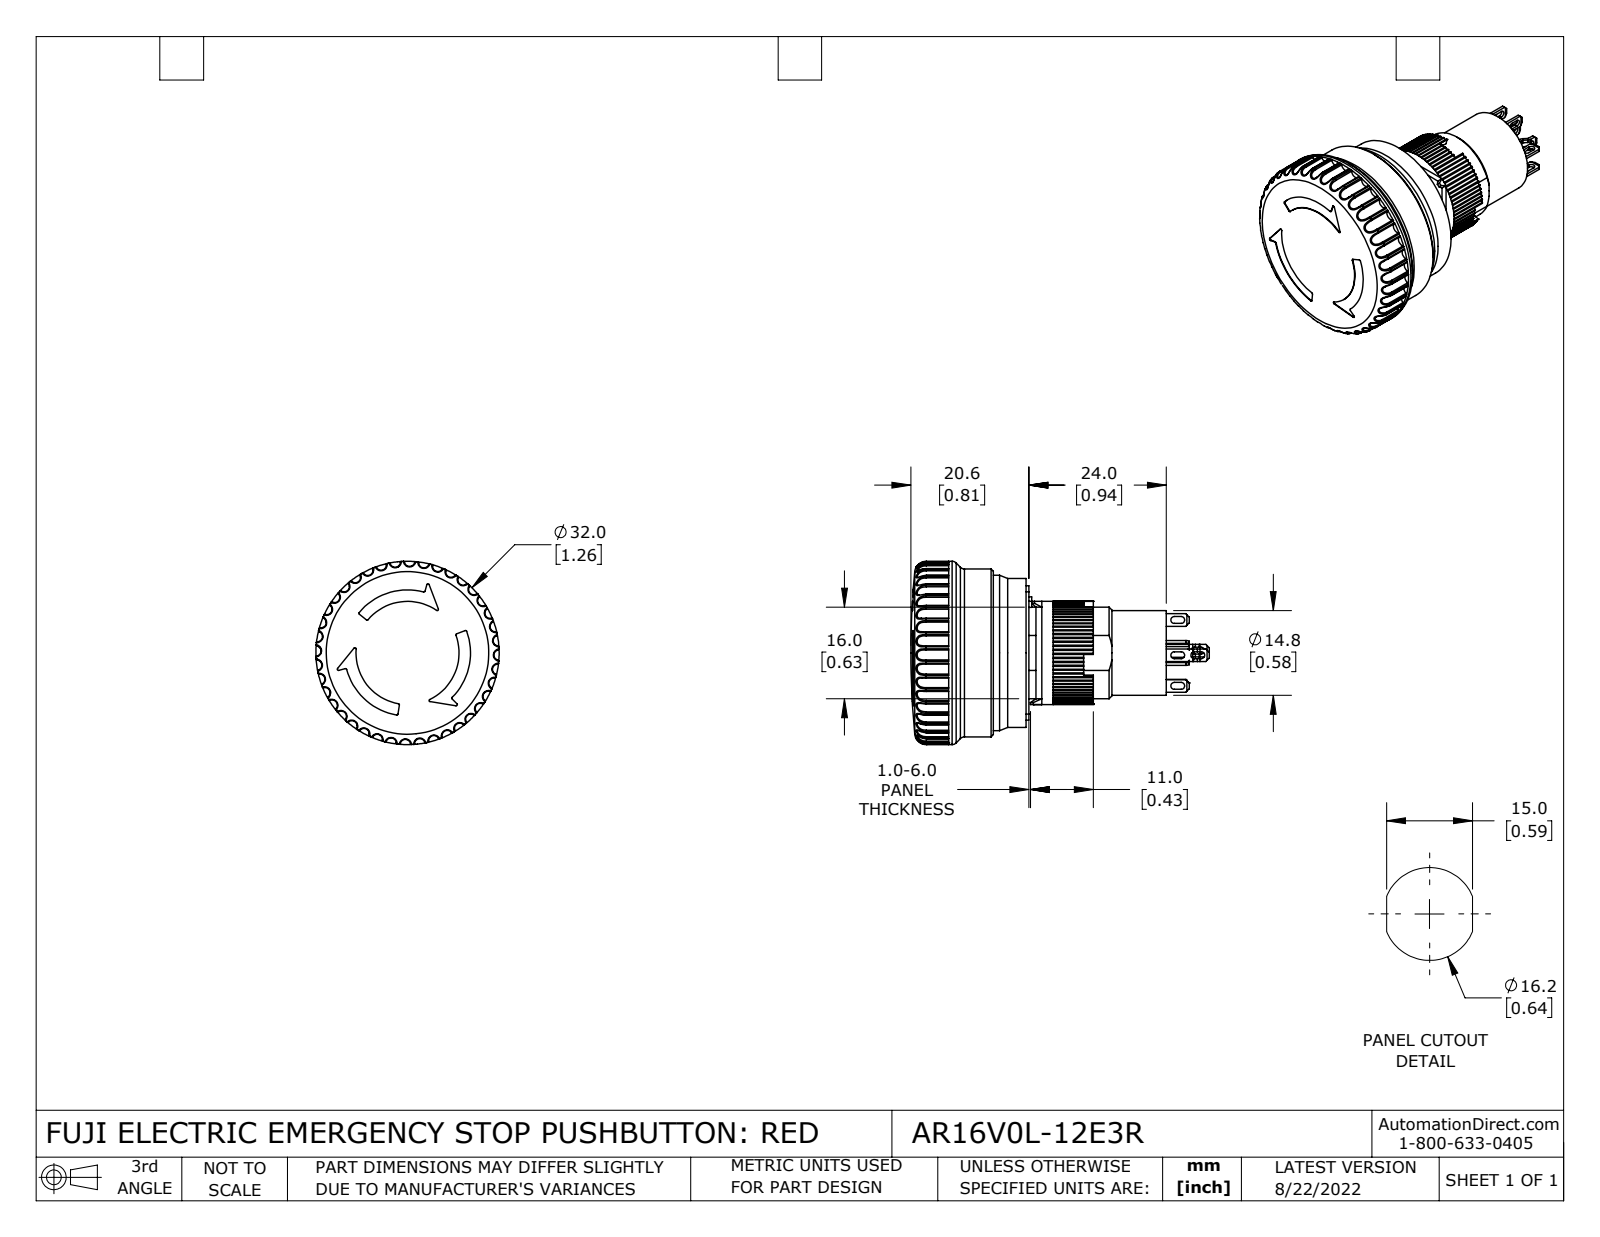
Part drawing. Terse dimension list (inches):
name: AR16V0L-12E3R
written by: SolidWorks 2021 (CONFIG_CONTROL_DESIGN)
unit: in
bodies: 7 solids, 1001 faces (540 planar, 387 cylindrical, 74 other)
size: 2.051 × 1.26 × 1.26
volume: 1.124 in³; area: 13.68 in²
holes: 1× ⌀0.583, 1× ⌀0.63, 1× ⌀1.069
bosses: 1× ⌀1.26, 1× ⌀1.154, 1× ⌀1.024, 1× ⌀0.858, 1× ⌀0.709, 1× ⌀0.236
rounds: 80× R0.008, 80× R0.01, 40× R0.035, 16× R0.024, 8× R0.02, 4× R0.01, 4× R0.029, 2× R0.039
face distances: 0.421, 0.53, 0.108, 0.039, 0.02, 0.069, 0.856, 0.49, 0.089, 0.049
